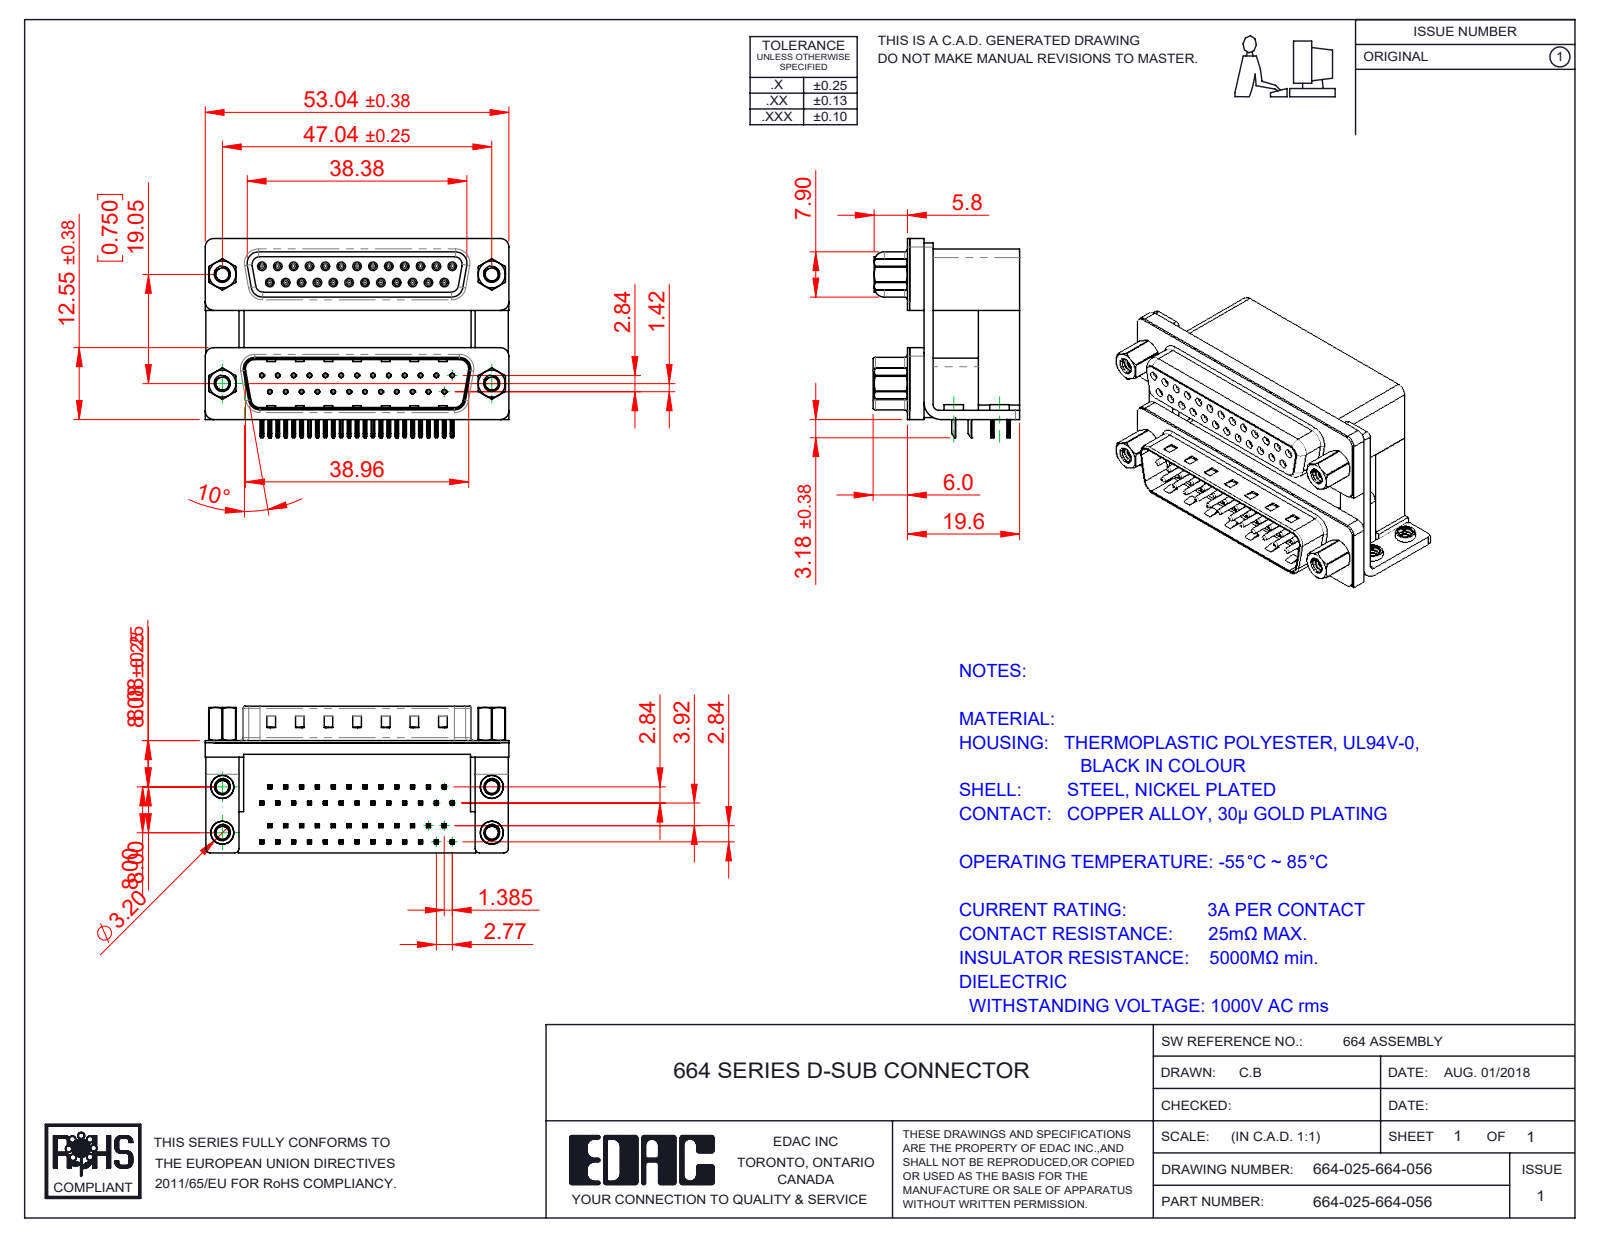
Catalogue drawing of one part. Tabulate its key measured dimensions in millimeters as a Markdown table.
| quantity | value |
| --- | --- |
| part name | 664 Threaded Rivet_4-40; 664 Housing Upper_25 Contacts M; 664 Housing Spacer_25 Contacts M; 664 Contact Bottom Lower (+8 more) |
| STEP written by | SolidWorks 2020 (CONFIG_CONTROL_DESIGN) |
| units | millimeters |
| bodies | 69 solids, 6595 faces (3313 planar, 1763 cylindrical, 1519 other) |
| overall size | 53.04 × 34.78 × 25.6 |
| volume | 22 952 mm³ |
| surface area | 25 284 mm² |
| round holes (diameter × count) | 0.8 × 50, 0.35 × 25, 0.9 × 25, 2.26 × 8, 2.29 × 4, 2.75 × 4, 3.2 × 4, 3.5 × 4, 4 × 4, 4.8 × 4, 5 × 4 |
| round bosses / shafts (diameter × count) | 1.2 × 25, 0.75 × 25, 4.9 × 4, 4.75 × 4, 4 × 4, 3.9 × 4, 3.4 × 4, 2.79 × 4 |
| partial cylindrical surfaces (radius × count) | 0.1 × 200, 0.15 × 100, 0.25 × 100, 0.12 × 50, 0.35 × 50, 0.34 × 25, 1.5 × 14, 0.28 × 12 |
| main face-to-face distances | 0.4, 19.2, 7.2, 12, 10.69, 16.7, 9.5, 2.5, 2.84, 18.71 |
| hole center spacings | 2.77, 3.16, 5.54, 8.31, 11.08, 13.85, 16.62, 5.03 |
